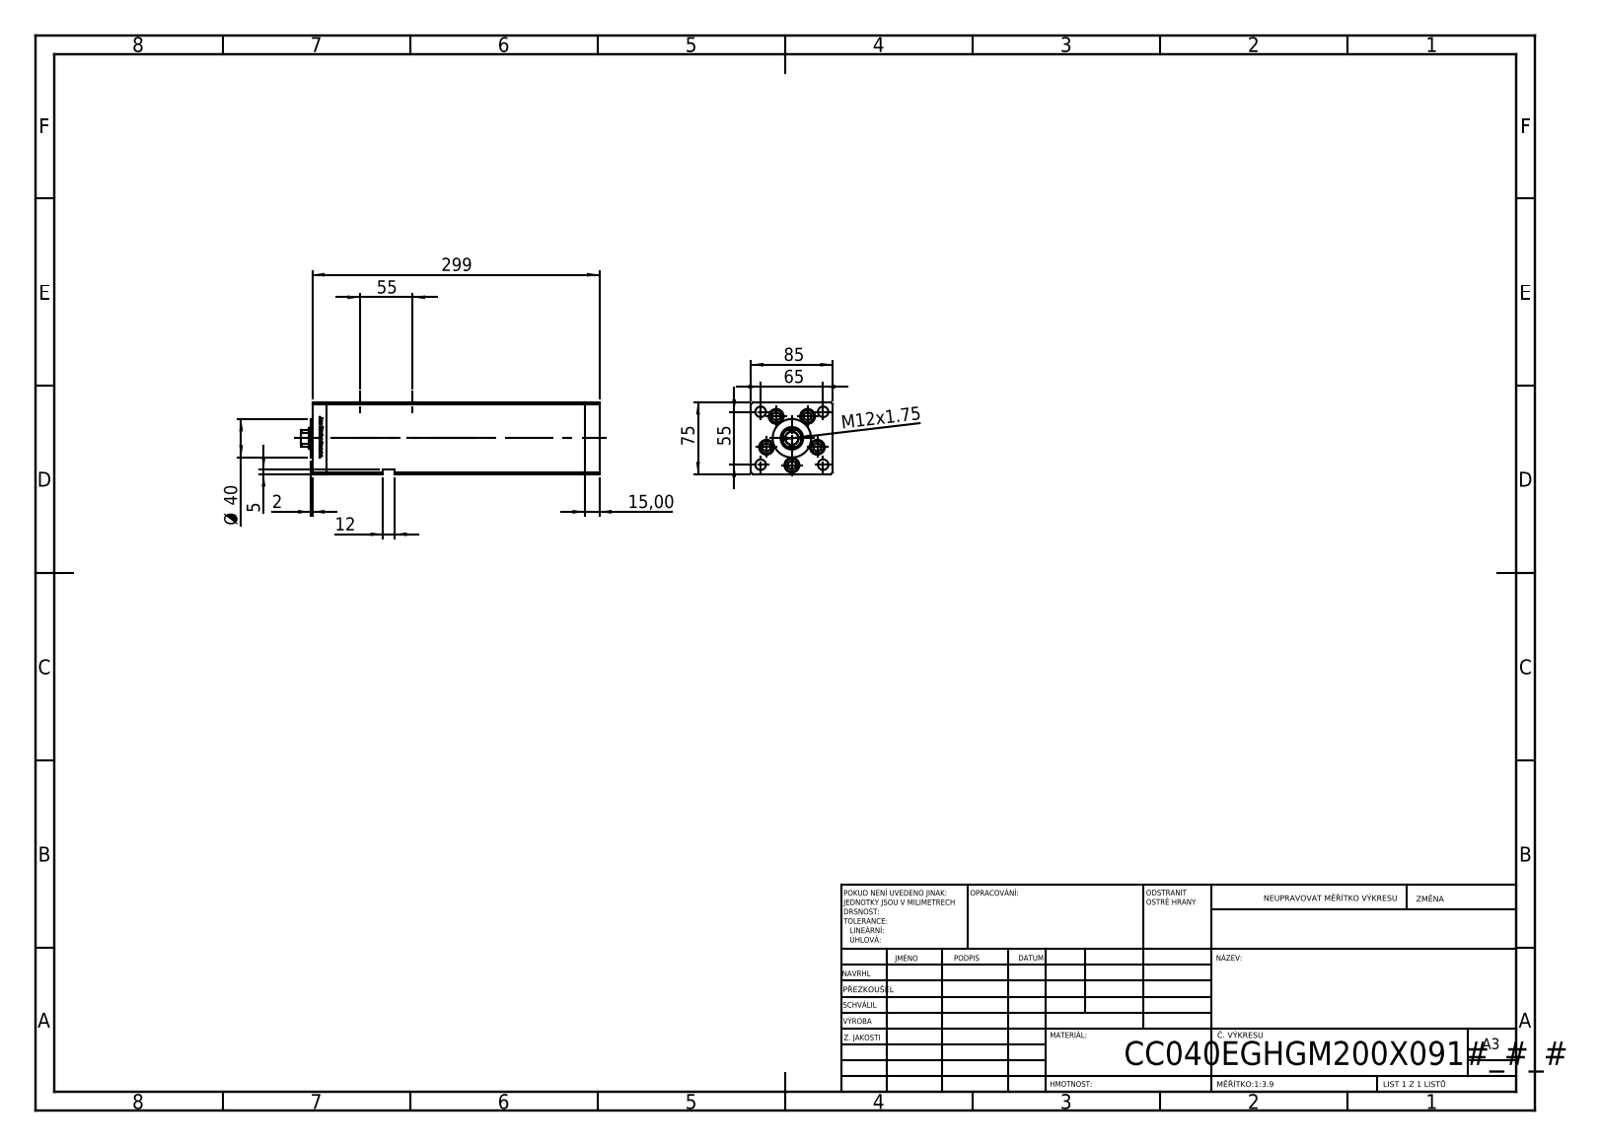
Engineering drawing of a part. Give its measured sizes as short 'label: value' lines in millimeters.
name: V220C_FRONT_E; V220C_E MIDDLE; ALLEN BOLT; V220C_VC_E (+1 more)
written by: SolidWorks 2019 (CONFIG_CONTROL_DESIGN)
unit: mm
bodies: 14 solids, 1212 faces (473 planar, 165 cylindrical, 574 other)
size: 310 × 85 × 75
volume: 1 606 000 mm³; area: 236 250 mm²
holes: 9× ⌀11, 5× ⌀15.5, 4× ⌀10.5, 4× ⌀16.5, 2× ⌀2, 2× ⌀13.16, 1× ⌀13.5, 1× ⌀22, 1× ⌀23.5
bosses: 5× ⌀14.5, 5× ⌀8, 1× ⌀40
rounds: 2× R0.93, 1× R10.5
face distances: 85, 75, 15, 268.5, 283.5, 10.5, 64.5, 298.5, 68.5, 31.25
hole spacings: 28, 42.57, 55, 65, 85.15, 16.86, 19.17, 32.33
